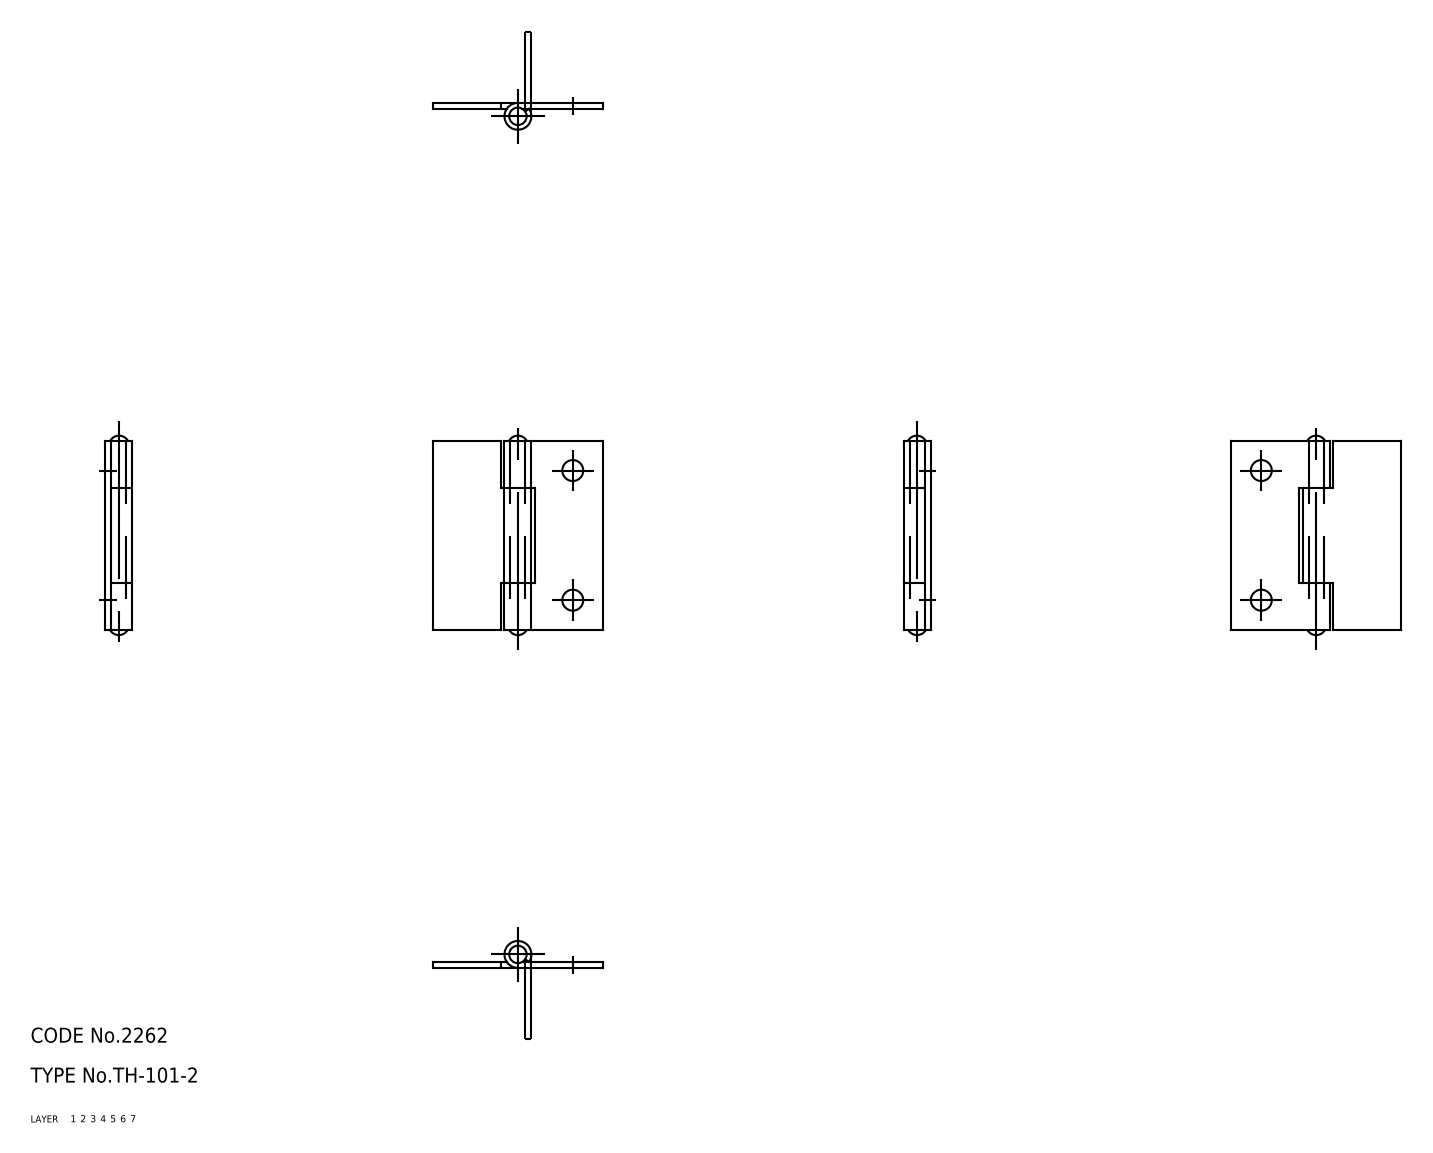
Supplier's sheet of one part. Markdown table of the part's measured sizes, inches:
| quantity | value |
| --- | --- |
| part name | 67110779; 67110792; 67110805 |
| STEP written by | CADfix (AUTOMOTIVE_DESIGN) |
| units | inches |
| bodies | 3 solids, 36 faces (0 planar, 0 cylindrical, 36 other) |
| overall size | 1.575 × 1.339 × 0.213 |
| volume | 0.131 in³ |
| surface area | 6.017 in² |
